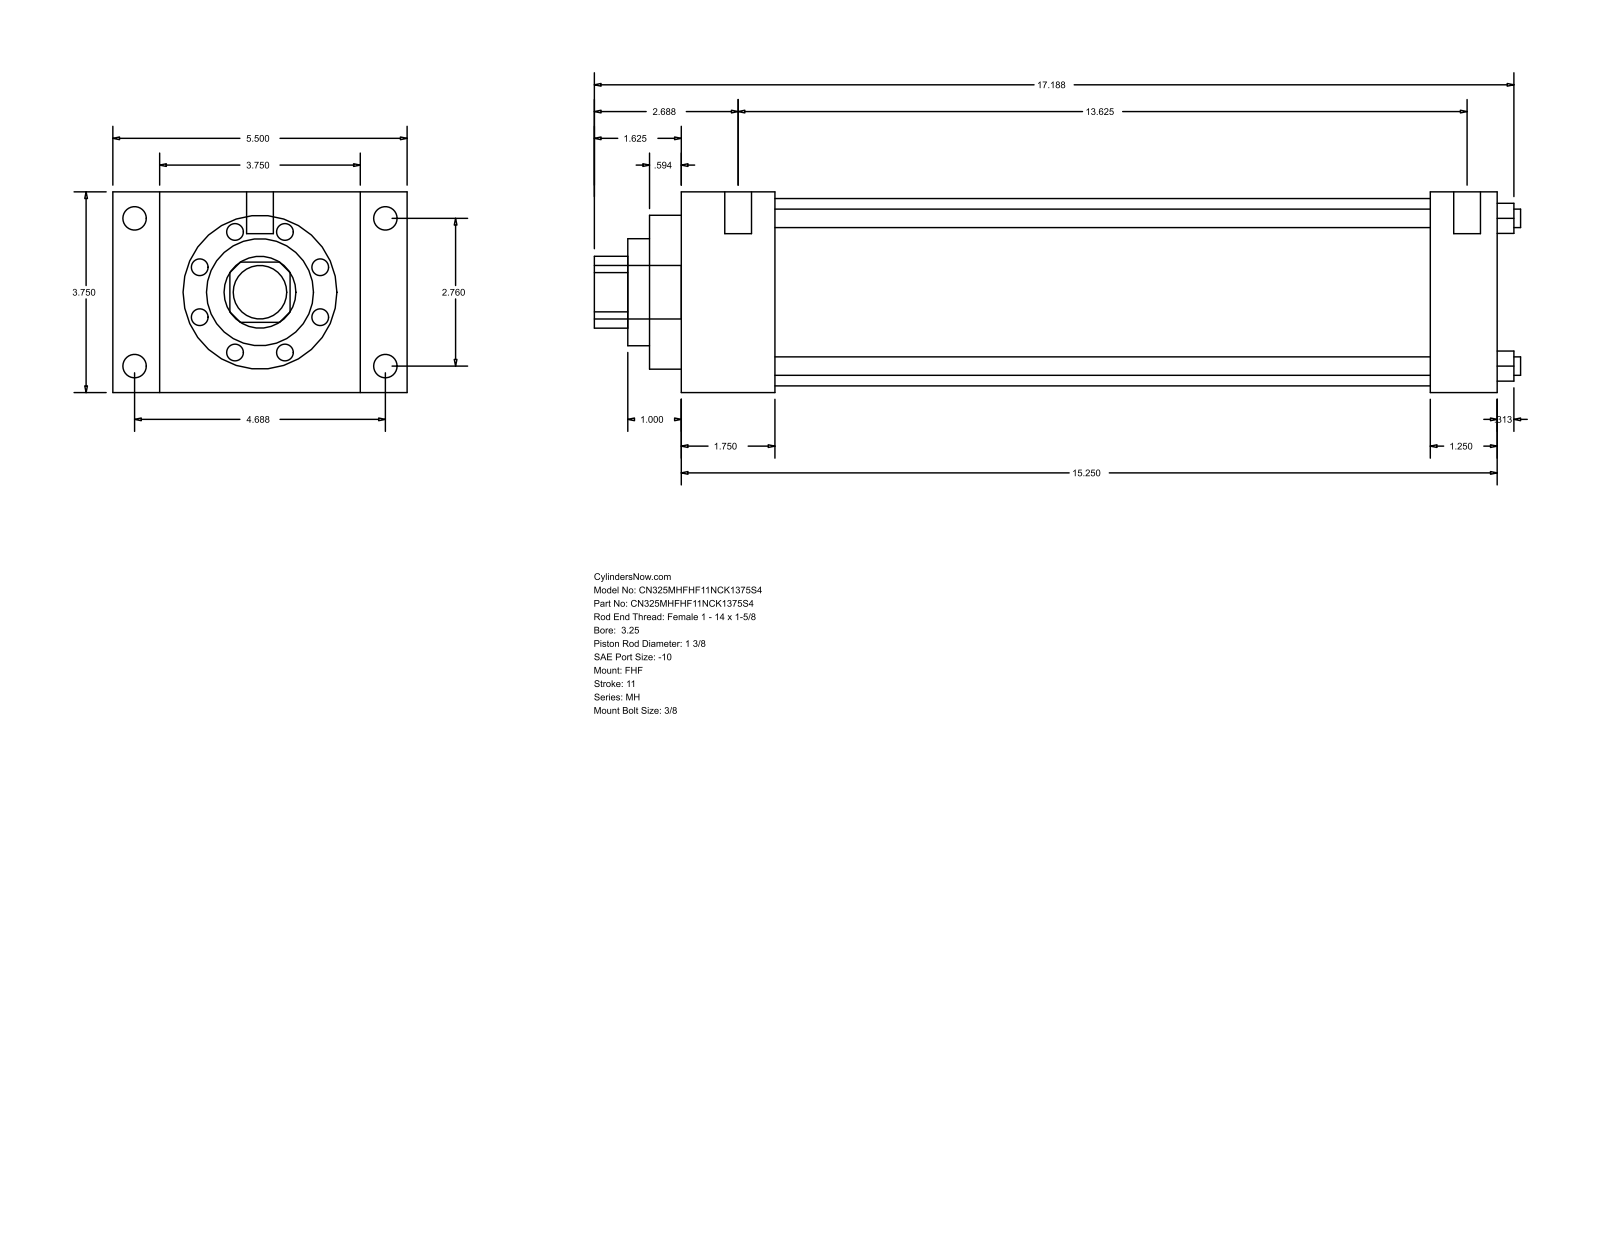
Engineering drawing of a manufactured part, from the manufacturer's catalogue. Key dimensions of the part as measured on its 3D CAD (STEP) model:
Part name (STEP PRODUCT): MH_FHF__0325_1.375
STEP written by: GSSL Pune (CONFIG_CONTROL_DESIGN)
Units: millimetres
Bodies: 0 solids, 90 faces (61 planar, 29 cylindrical, 0 other)
Overall size (bounding box): 439.74 × 139.7 × 95.25
Round holes (diameter × count): ⌀8.76 ×4, ⌀34.92 ×1, ⌀50.8 ×1, ⌀73.03 ×1, ⌀88.9 ×1
Round bosses / shafts (diameter × count): ⌀11.13 ×4, ⌀5.56 ×4, ⌀12.7 ×2, ⌀25.4 ×1
Partial cylindrical surfaces — rounded edges, fillets, slot ends (radius × count): R17.06 ×1
Main face-to-face distances: 95.24, 387.35, 44.45, 342.9, 22.23, 117.47, 139.7, 355.61, 311.16, 31.74
Hole centre spacings: 49.57, 70.1, 99.14
